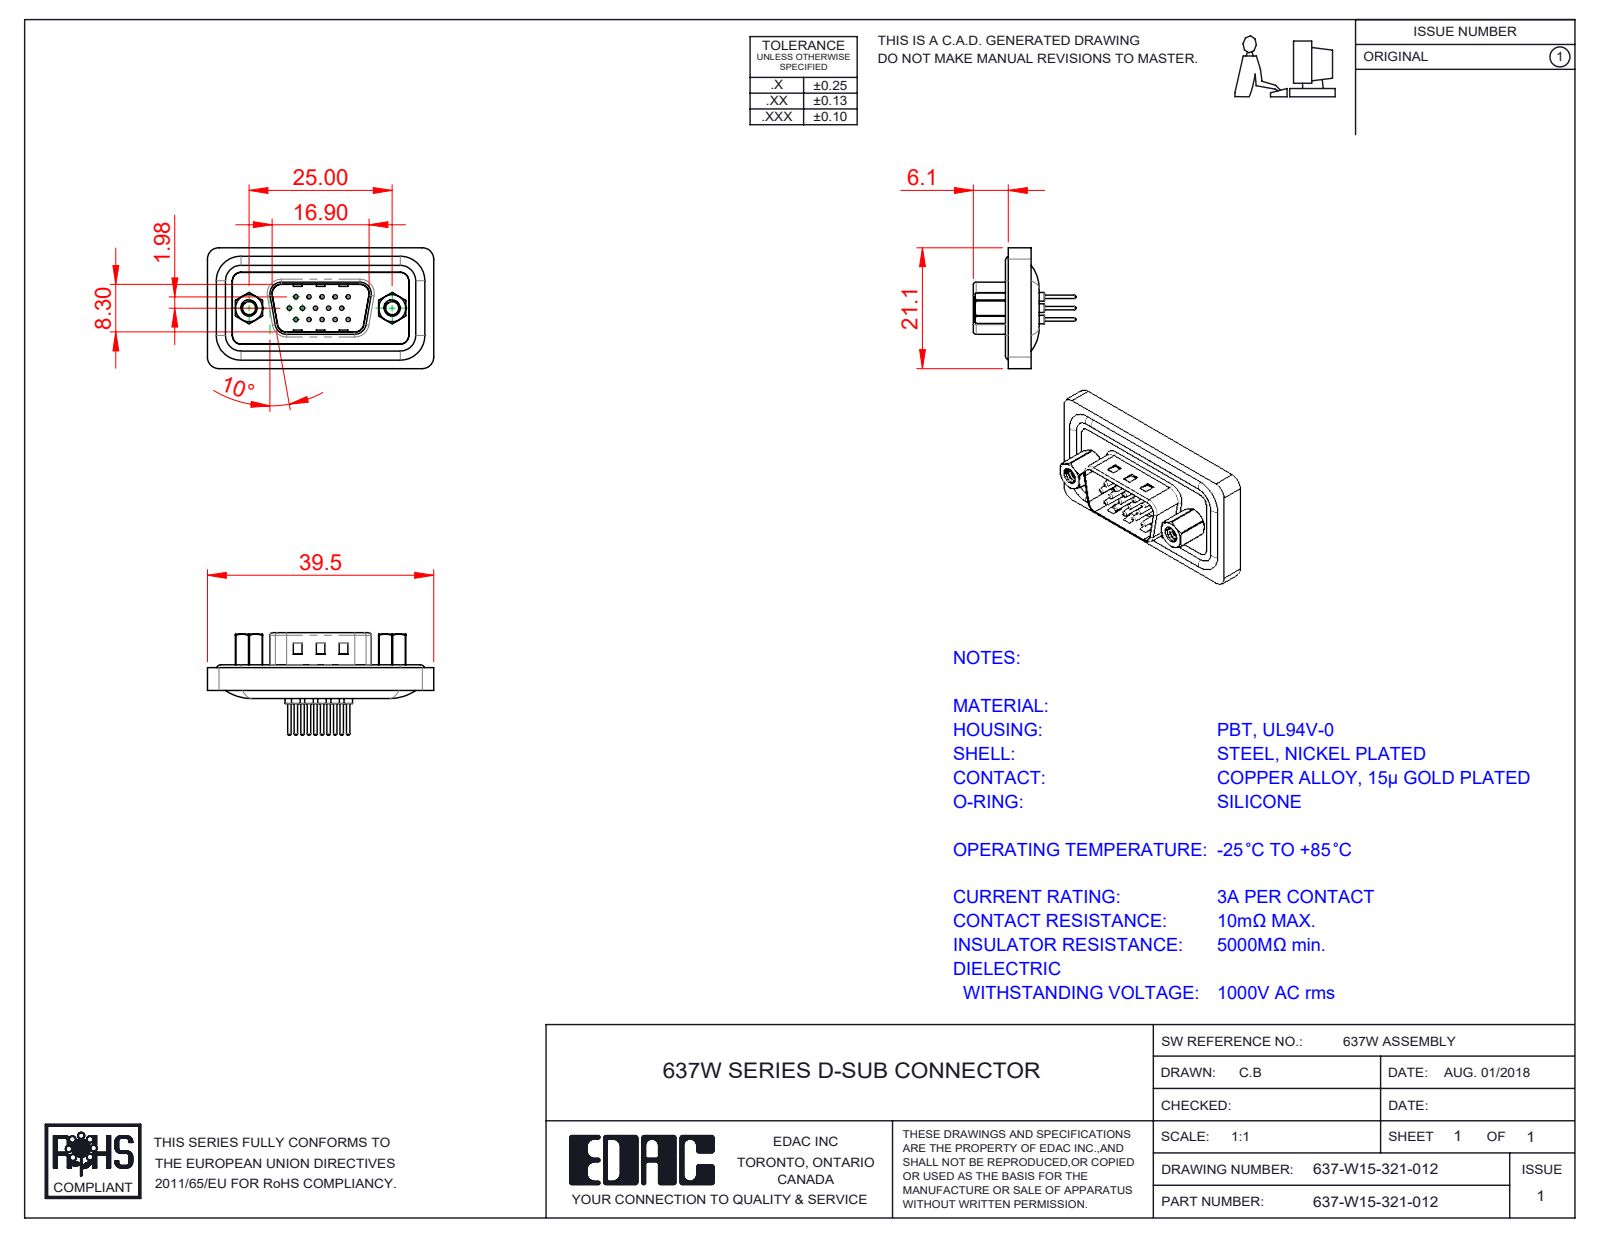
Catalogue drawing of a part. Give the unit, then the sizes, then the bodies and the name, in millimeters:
Units: millimetres
Overall size (bounding box): 39.51 × 21.1 × 18.1
Round holes (diameter × count): ⌀0.75 ×15, ⌀1.5 ×15, ⌀1.6 ×15, ⌀2 ×15, ⌀2.26 ×2, ⌀2.29 ×2, ⌀4 ×2, ⌀4.8 ×2, ⌀5 ×2
Round bosses / shafts (diameter × count): ⌀0.6 ×15, ⌀1.5 ×8, ⌀1.6 ×4, ⌀4.9 ×2, ⌀2.79 ×2, ⌀5 ×1
Partial cylindrical surfaces — rounded edges, fillets, slot ends (radius × count): R1.5 ×14, R2 ×14, R0.5 ×8, R2.7 ×6, R0.9 ×4, R1.6 ×4, R4.3 ×4, R0.4 ×2
Main face-to-face distances: 0.4, 1.6, 1.1, 2.9, 2.5, 0.5, 4, 3.6, 3.4, 0.7
Hole centre spacings: 3.96, 2.28, 4.57, 2.29, 6.05, 6.04, 7.92, 6.86
Volume: 3 988 mm³ · Surface area: 6 804 mm²
Bodies: 23 solids, 1033 faces (246 planar, 452 cylindrical, 335 other)
Part name (STEP PRODUCT): 637W Contact Row 2_21; 637W Housing_15 Contacts; 637-W15-321-012; 637W 4-40 Hex Standoff (+5 more)
STEP written by: SolidWorks 2023 (CONFIG_CONTROL_DESIGN)
